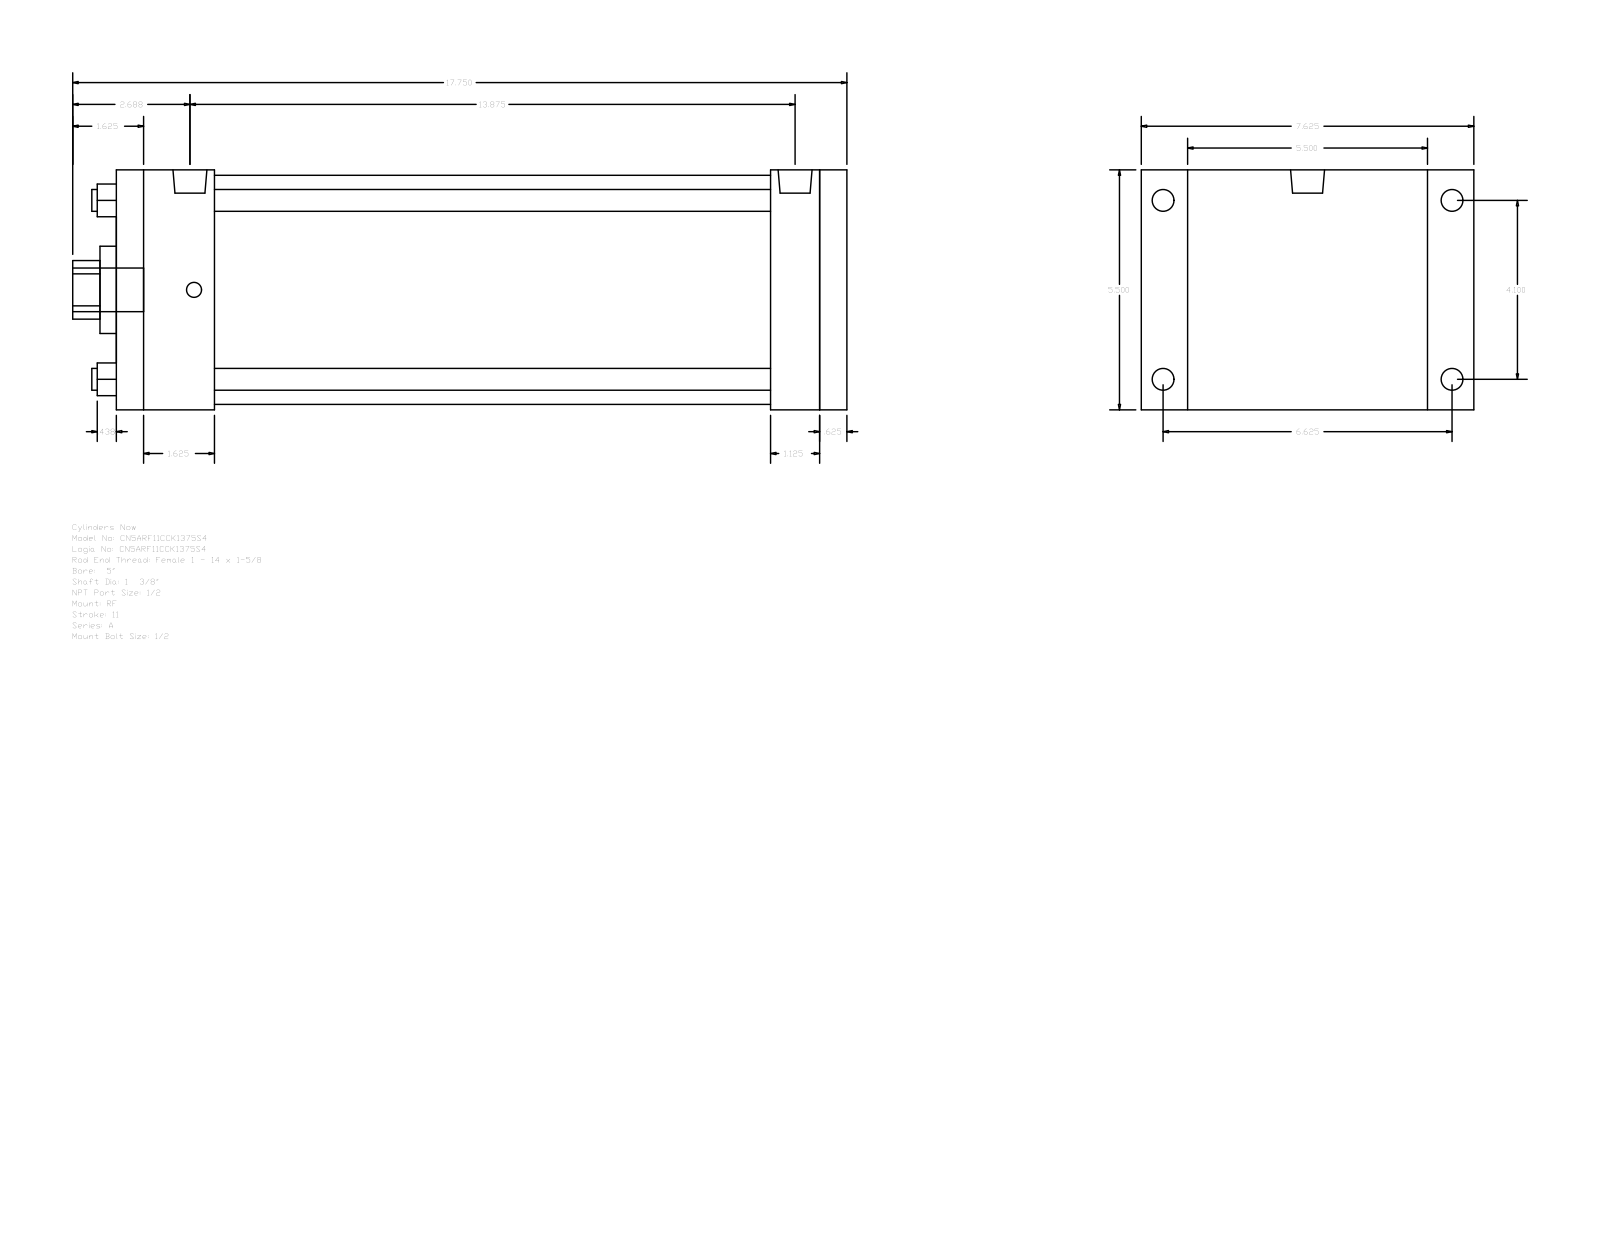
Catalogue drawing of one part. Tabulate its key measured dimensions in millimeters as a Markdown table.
| quantity | value |
| --- | --- |
| part name | A_RF__0500_1.375 |
| STEP written by | GSSL Pune (CONFIG_CONTROL_DESIGN) |
| units | millimeters |
| bodies | 0 solids, 92 faces (64 planar, 28 cylindrical, 0 other) |
| overall size | 450.85 × 193.68 × 139.7 |
| round holes (diameter × count) | 12.7 × 4, 34.92 × 1, 50.8 × 1, 133.35 × 1 |
| round bosses / shafts (diameter × count) | 12.7 × 4, 8.73 × 4, 19.77 × 2, 25.4 × 1 |
| partial cylindrical surfaces (radius × count) | 17.06 × 1 |
| main face-to-face distances | 139.7, 425.45, 15.87, 409.58, 28.58, 57.15, 352.43, 368.3, 381, 323.85 |
| hole center spacings | 73.64, 104.14, 147.28 |
